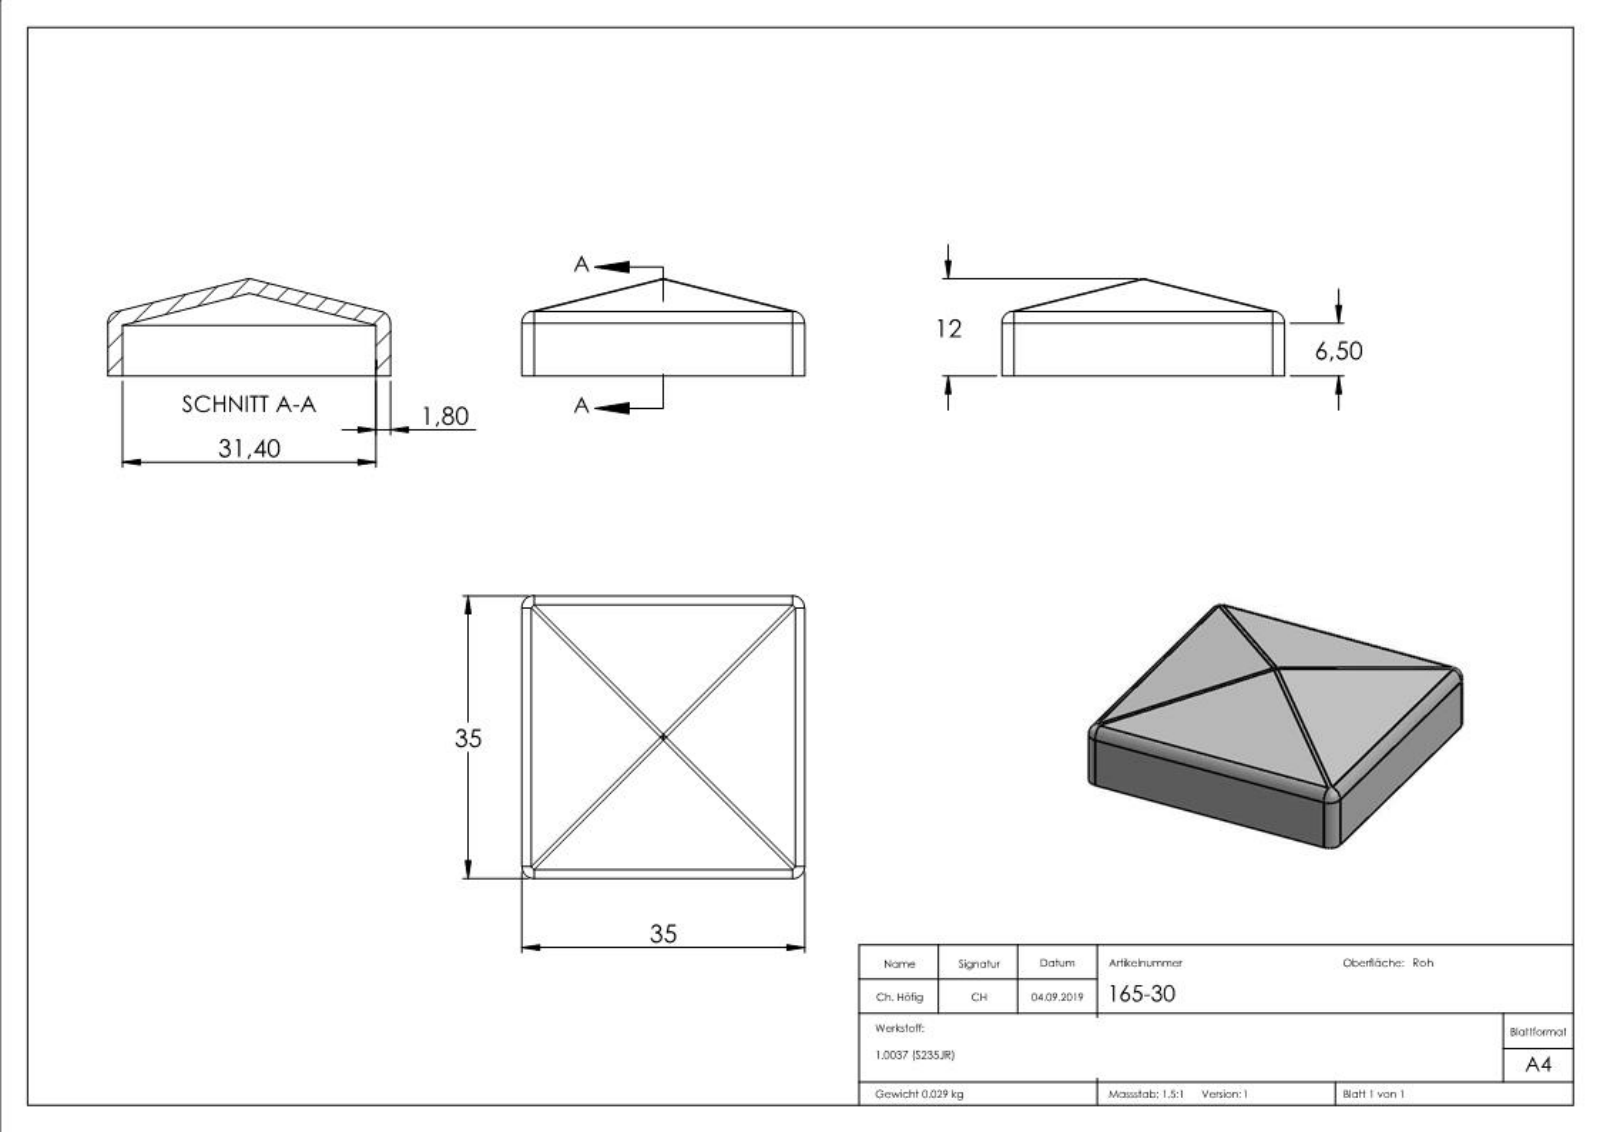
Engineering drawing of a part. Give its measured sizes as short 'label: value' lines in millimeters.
name: 165-30
written by: SolidWorks 2015 (CONFIG_CONTROL_DESIGN)
unit: mm
bodies: 1 solid, 322 faces (170 planar, 12 cylindrical, 140 other)
size: 35 × 35 × 12
volume: 3 664 mm³; area: 4 317 mm²
rounds: 12× R1.5
face distances: 1.8, 33.2, 35, 31.4, 1.7, 31.5, 33.3, 6.36, 1, 0.58
